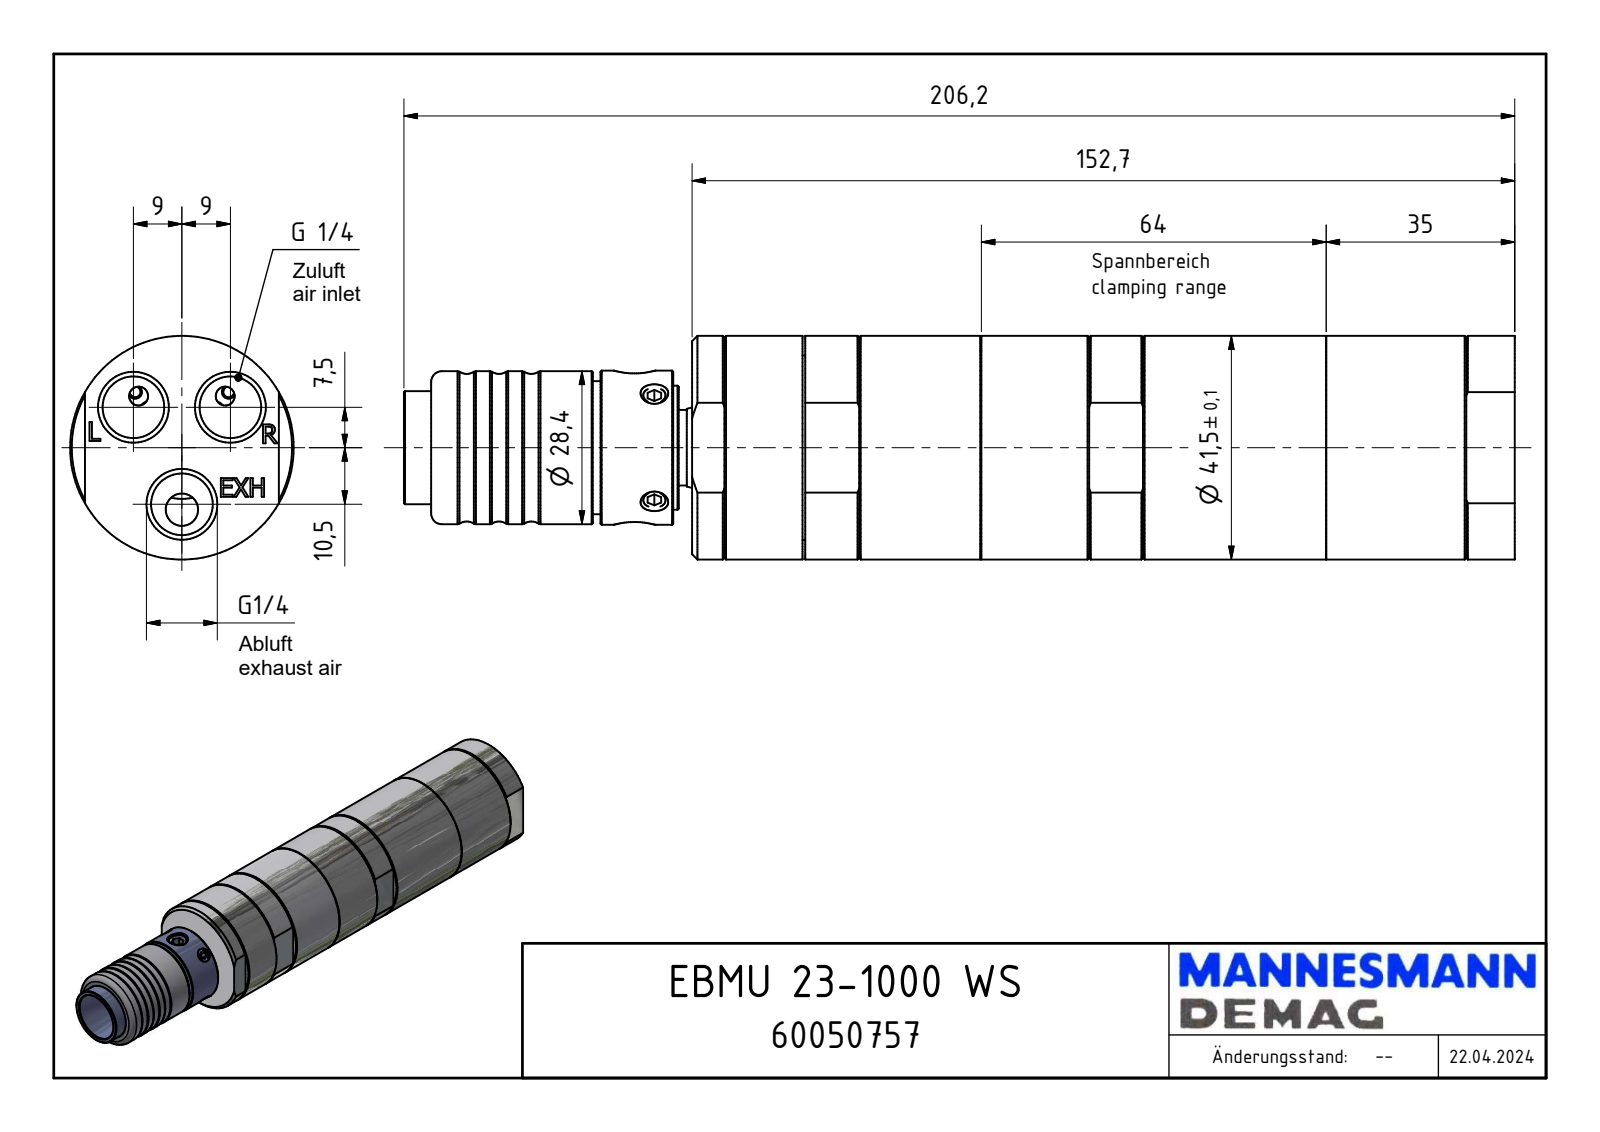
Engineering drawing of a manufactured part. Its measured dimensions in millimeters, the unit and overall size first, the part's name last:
Units: millimetres
Overall size (bounding box): 206.2 × 41.5 × 41.5
Round holes (diameter × count): ⌀11.45 ×3, ⌀6.65 ×1, ⌀9 ×1, ⌀14 ×1, ⌀16 ×1, ⌀21.1 ×1, ⌀27.4 ×1
Round bosses / shafts (diameter × count): ⌀41.5 ×1, ⌀37.99 ×1, ⌀28.6 ×1, ⌀28.4 ×1, ⌀26 ×1, ⌀23 ×1, ⌀21 ×1, ⌀14.95 ×1
Partial cylindrical surfaces — rounded edges, fillets, slot ends (radius × count): R2.07 ×2, R2.5 ×2, R8.21 ×1, R17 ×1
Main face-to-face distances: 152.7, 1, 38, 37, 5, 147.7, 53.5, 2.5, 127.2, 0.5
Hole centre spacings: 11.72, 20.12, 10.5, 18
Volume: 229 940 mm³ · Surface area: 31 568 mm²
Bodies: 1 solid, 272 faces (156 planar, 61 cylindrical, 55 other)
Part name (STEP PRODUCT): EBMU 23-1000 WS_60050757
STEP written by: Autodesk Inventor 2024 (AUTOMOTIVE_DESIGN)
